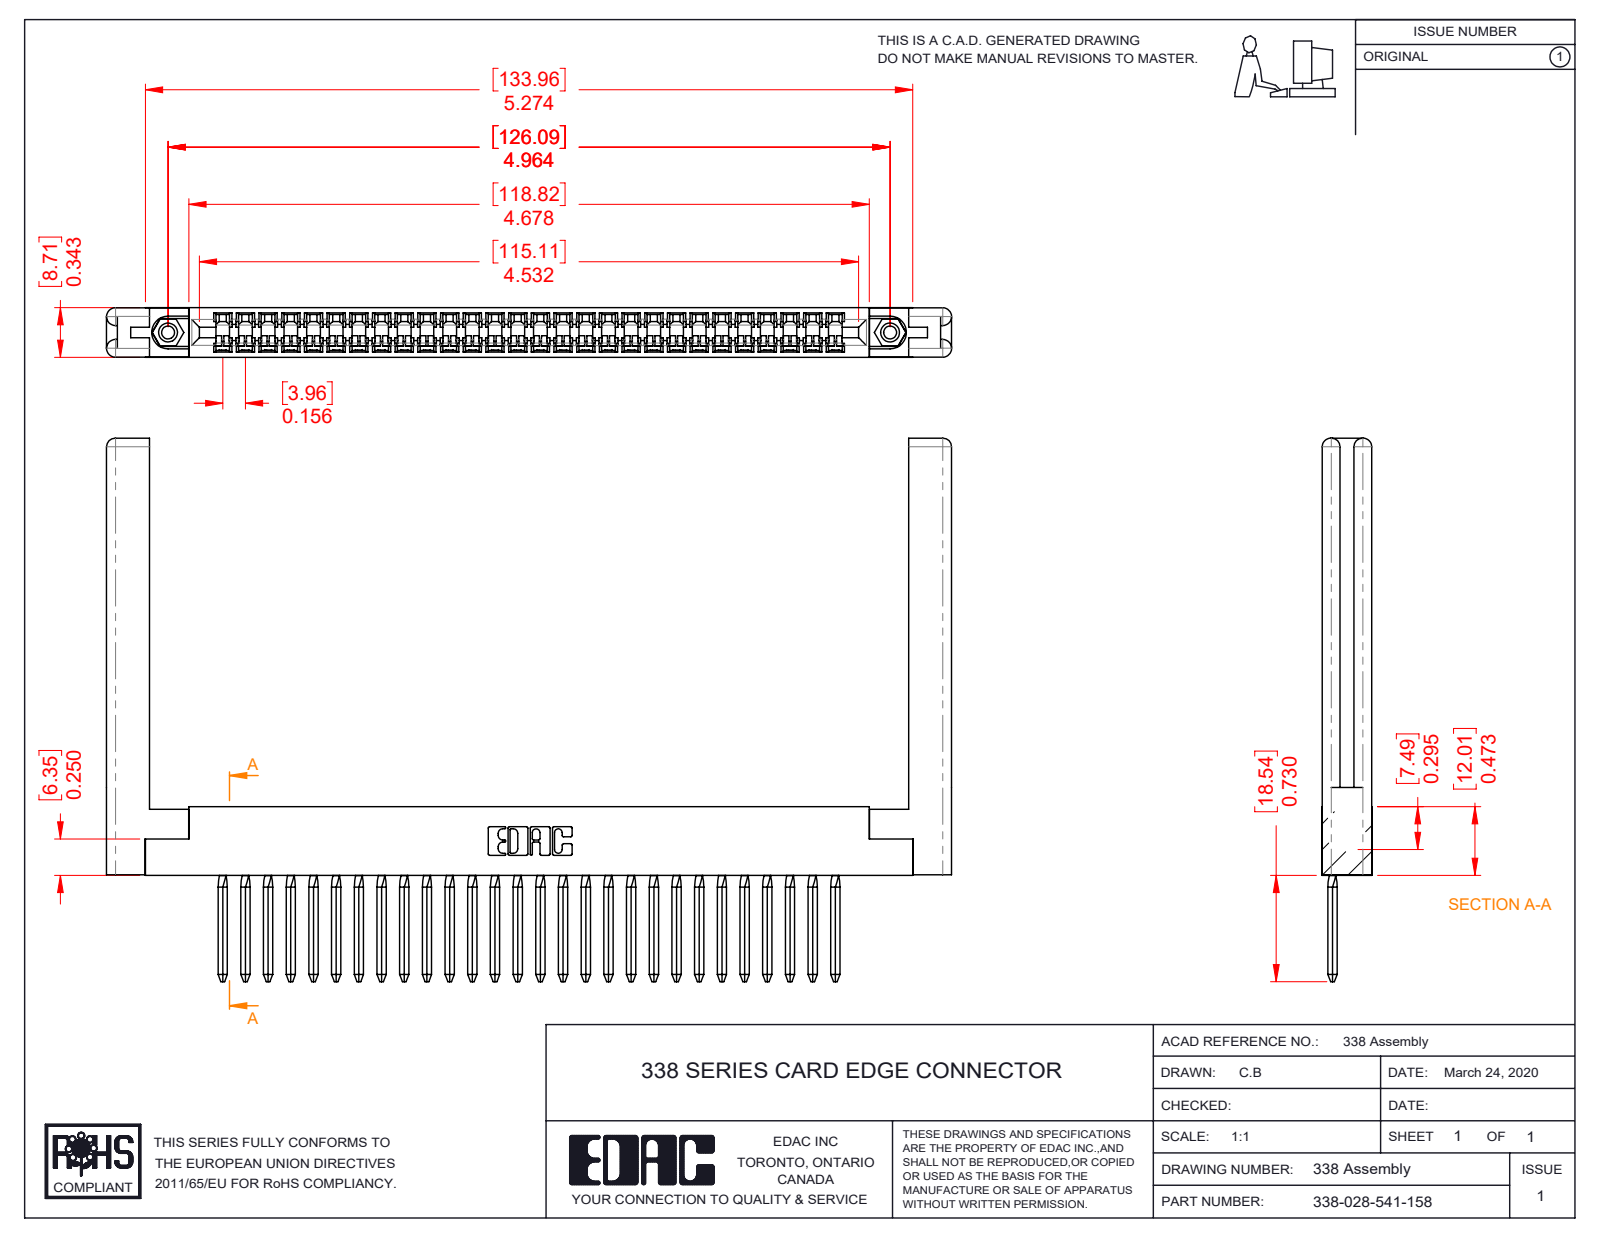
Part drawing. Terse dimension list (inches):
name: 307-220-058; 338-210-001_338-210-028-004; 345-250-001_345-250-001-102; 338-290-001_541 (+1 more)
written by: SolidWorks 2016 (CONFIG_CONTROL_DESIGN)
unit: in
bodies: 33 solids, 2840 faces (1954 planar, 750 cylindrical, 136 other)
size: 5.81 × 3.735 × 0.343
volume: 1.097 in³; area: 34.2 in²
holes: 2× ⌀0.089, 2× ⌀0.125, 2× ⌀0.156
bosses: 2× ⌀0.155
rounds: 114× R0.025, 28× R0.008, 23× R0.055, 23× R0.067, 22× R0.01, 22× R0.1, 8× R0.061, 6× R0.007
face distances: 0.341, 0.343, 0.34, 0.136, 0.207, 0.134, 0.206, 0.22, 0.091, 0.295
hole spacings: 4.964
